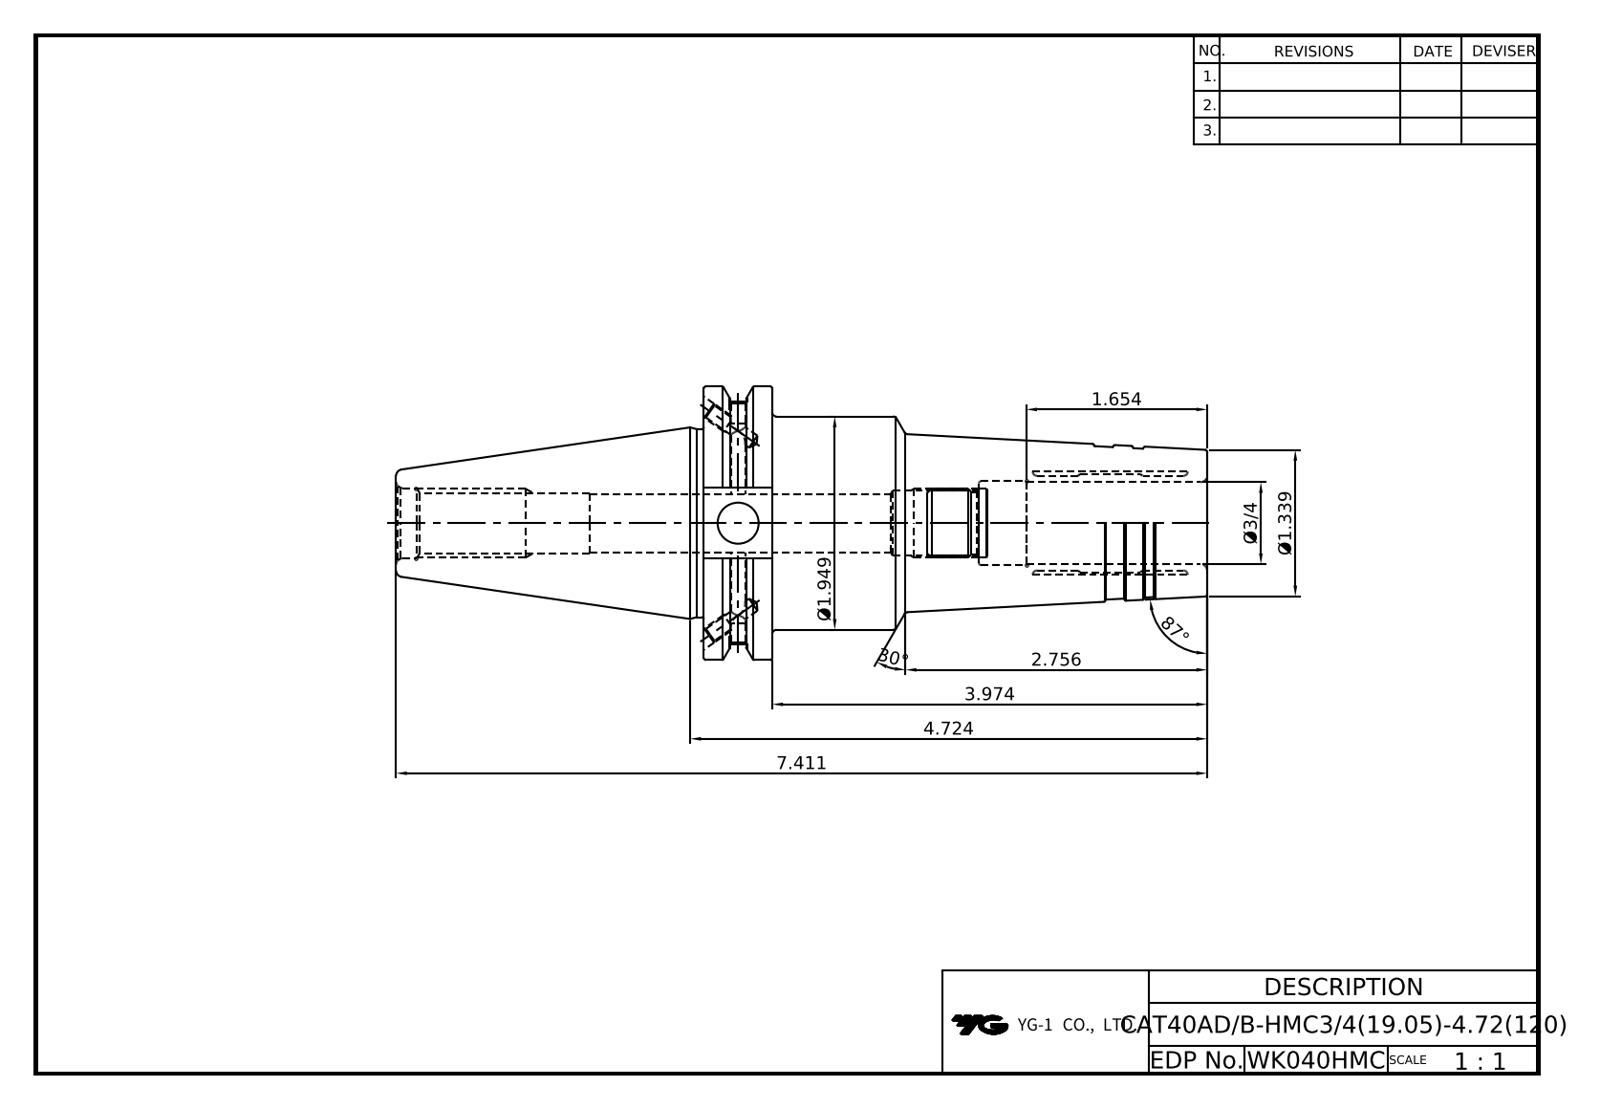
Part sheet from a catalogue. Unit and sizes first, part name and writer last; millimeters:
Units: millimetres
Overall size (bounding box): 188.25 × 63.5 × 61.09
Round holes (diameter × count): ⌀3.24 ×4, ⌀4 ×2, ⌀4.2 ×2, ⌀9.53 ×1, ⌀13 ×1, ⌀13.39 ×1, ⌀14.92 ×1, ⌀16.3 ×1, ⌀19.05 ×1, ⌀19.4 ×1
Round bosses / shafts (diameter × count): ⌀63.5 ×1, ⌀49.5 ×1, ⌀43.6 ×1
Partial cylindrical surfaces — rounded edges, fillets, slot ends (radius × count): R8.19 ×1, R28.15 ×1
Main face-to-face distances: 15.88, 116.83, 100.95, 47.6, 16.38, 71.42, 87.3, 188.25, 135.25, 63.83
Volume: 214 938 mm³ · Surface area: 38 344 mm²
Bodies: 1 solid, 106 faces (36 planar, 30 cylindrical, 40 other)
Part name (STEP PRODUCT): LO-CAT40ADB-HMC19.05-120
STEP written by: Autodesk Inventor 2020 (AUTOMOTIVE_DESIGN)
